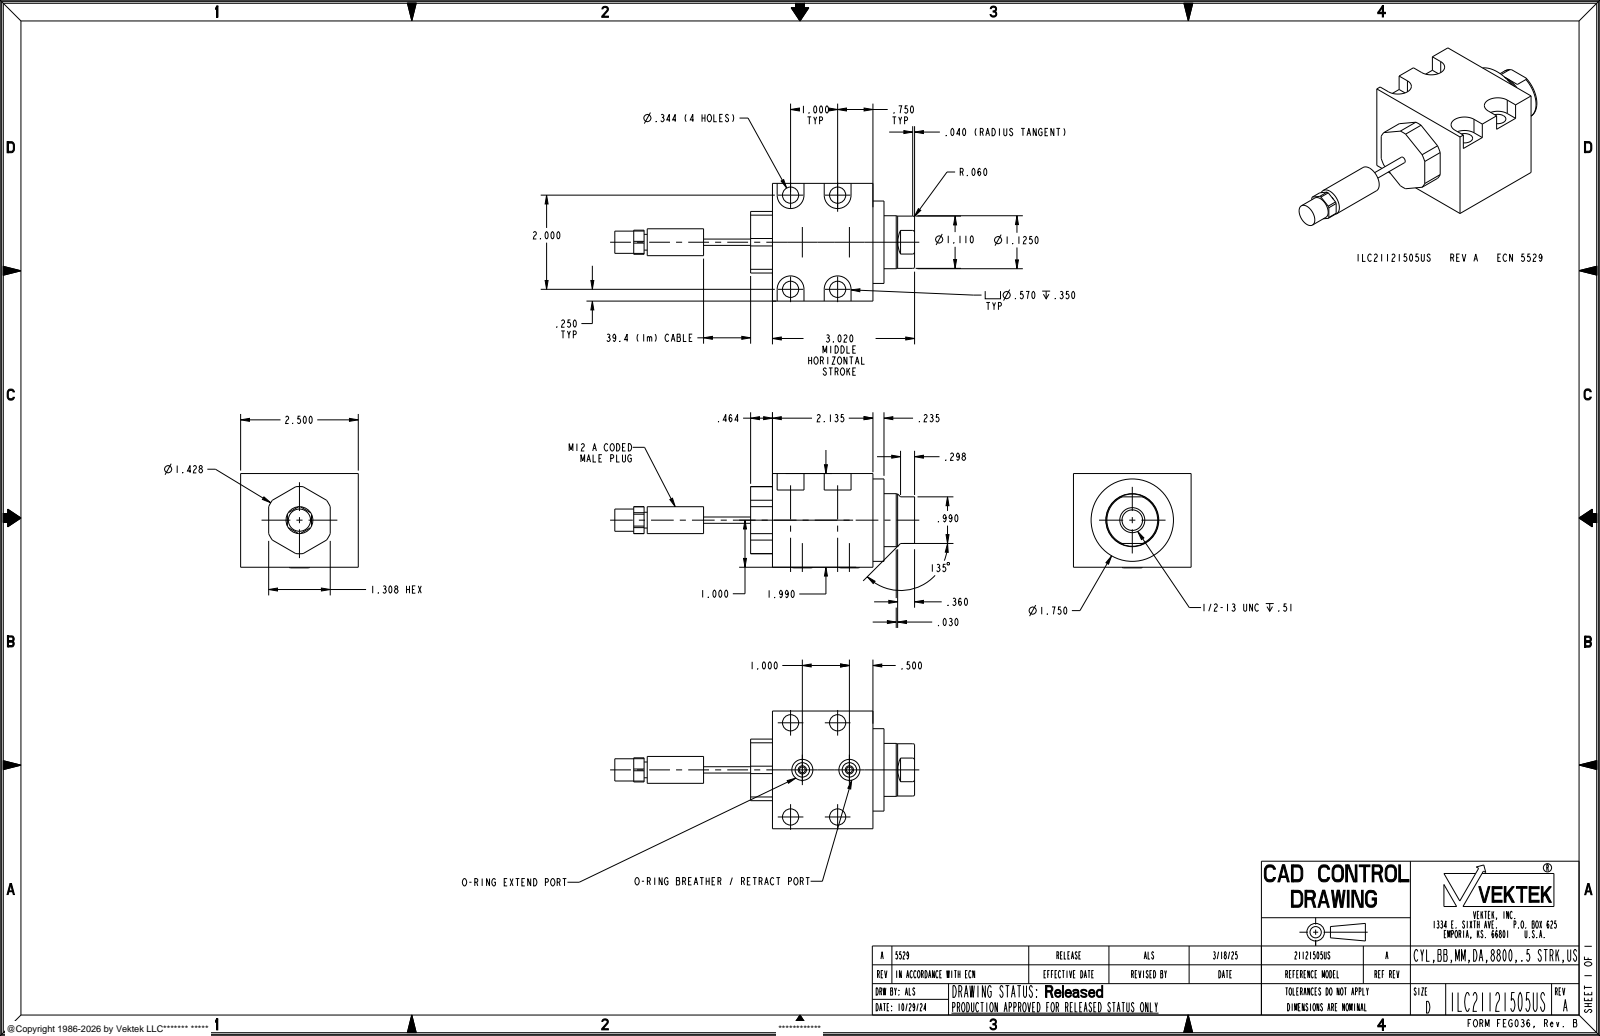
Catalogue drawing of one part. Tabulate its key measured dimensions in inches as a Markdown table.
| quantity | value |
| --- | --- |
| part name | ILC21121505US |
| STEP written by | CREO PARAMETRIC BY PTC INC, 2021164 (AUTOMOTIVE_DESIGN) |
| units | inches |
| bodies | 1 solid, 120 faces (46 planar, 52 cylindrical, 22 other) |
| overall size | 6.37 × 2.7 × 2.003 |
| volume | 11.82 in³ |
| surface area | 49.21 in² |
| round holes (diameter × count) | 0.344 × 4, 0.125 × 2, 0.447 × 2, 0.437 × 1 |
| round bosses / shafts (diameter × count) | 1.75 × 1, 1.125 × 1, 1.11 × 1, 0.571 × 1, 0.5 × 1, 0.472 × 1, 0.335 × 1, 0.134 × 1 |
| partial cylindrical surfaces (radius × count) | 0.285 × 4, 0.714 × 1 |
| main face-to-face distances | 1.99, 2.5, 2.135, 2.599, 0.464, 0.235, 2.37, 2.834, 1.308, 1.64 |
| hole center spacings | 1.031, 1, 1.25, 1.601, 2, 2.236 |
